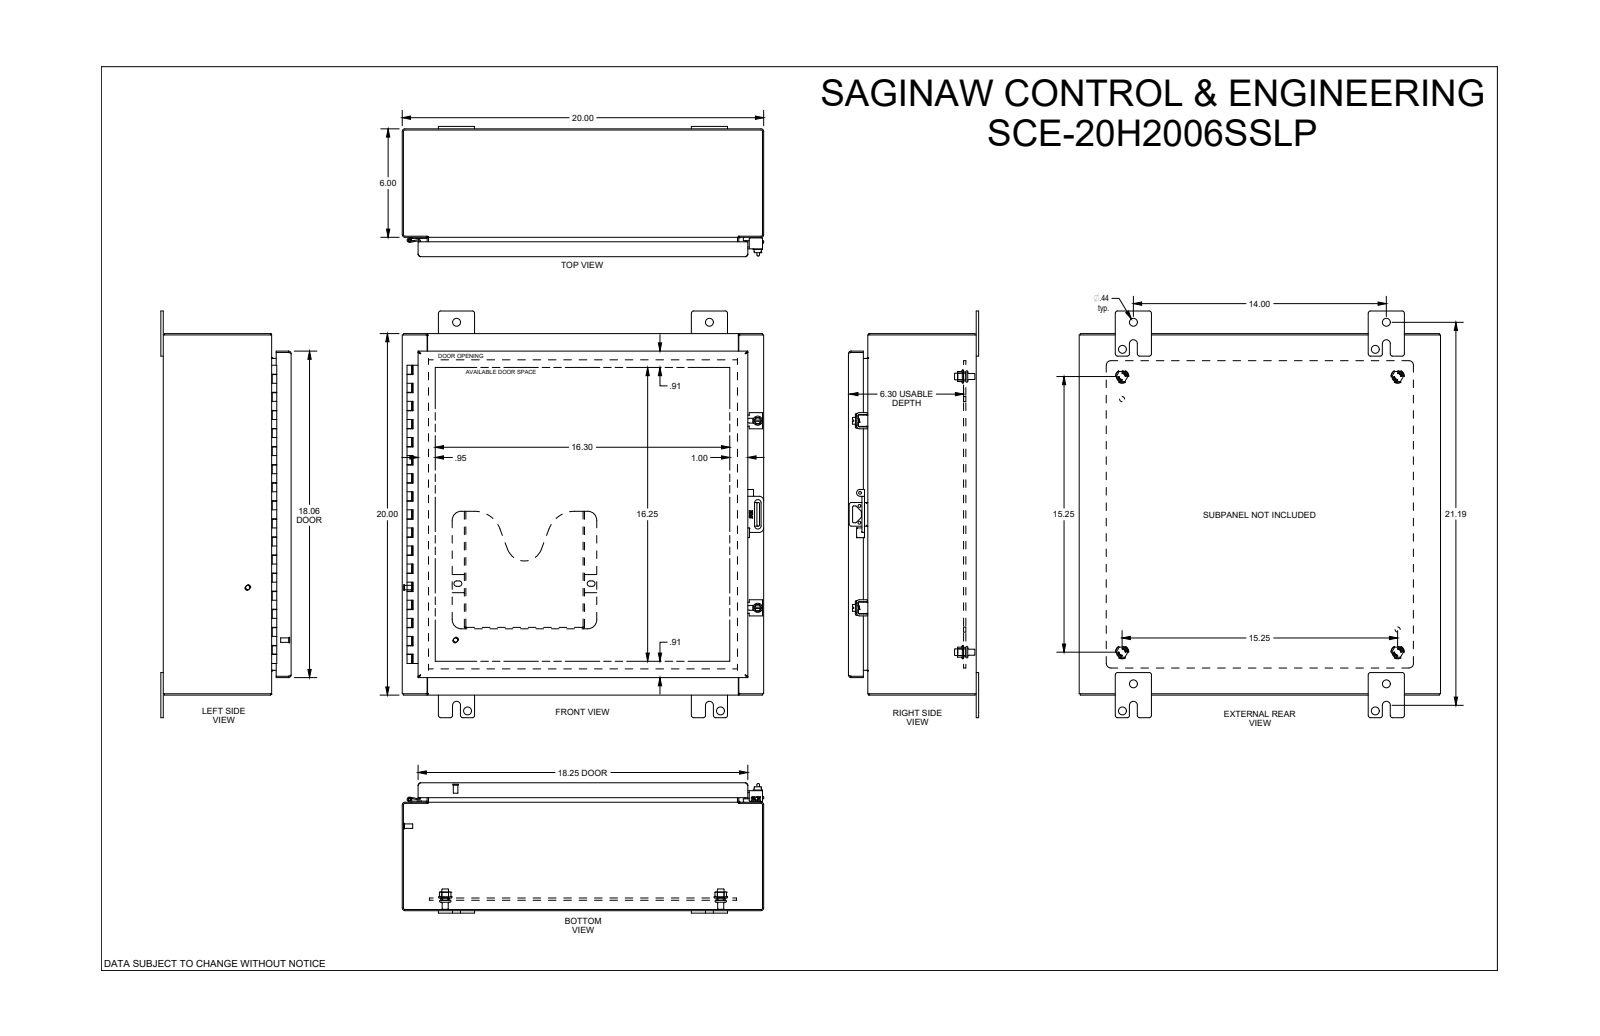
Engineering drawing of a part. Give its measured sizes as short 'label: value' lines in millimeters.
name: SCE-20H2006SSLP
written by: SolidWorks 2019 (CONFIG_CONTROL_DESIGN)
unit: mm
bodies: 0 solids, 3015 faces (1210 planar, 622 cylindrical, 1183 other)
size: 571.5 × 508 × 183.1
holes: 8× ⌀11.1, 5× ⌀6.4, 4× ⌀9.3, 4× ⌀12.7, 3× ⌀4.8, 3× ⌀4.9, 2× ⌀4.1, 2× ⌀5.2, 2× ⌀7.1, 1× ⌀3.3, 1× ⌀3.4
bosses: 7× ⌀6.3, 5× ⌀14.3, 4× ⌀9.3, 4× ⌀8.4, 3× ⌀6.5, 3× ⌀6.4, 3× ⌀4.8, 2× ⌀12.9
rounds: 108× R0.3, 36× R0.4, 30× R0.7, 27× R0.8, 27× R3.2, 25× R1.5, 22× R1, 14× R1.8
face distances: 1.9, 506.1, 177.7, 175.8, 1.9, 179.7, 177.7, 12.7, 15.9, 3.2
hole spacings: 355.6, 387.4, 77.9, 13.1, 31.8, 36.6, 41.1, 41.1
